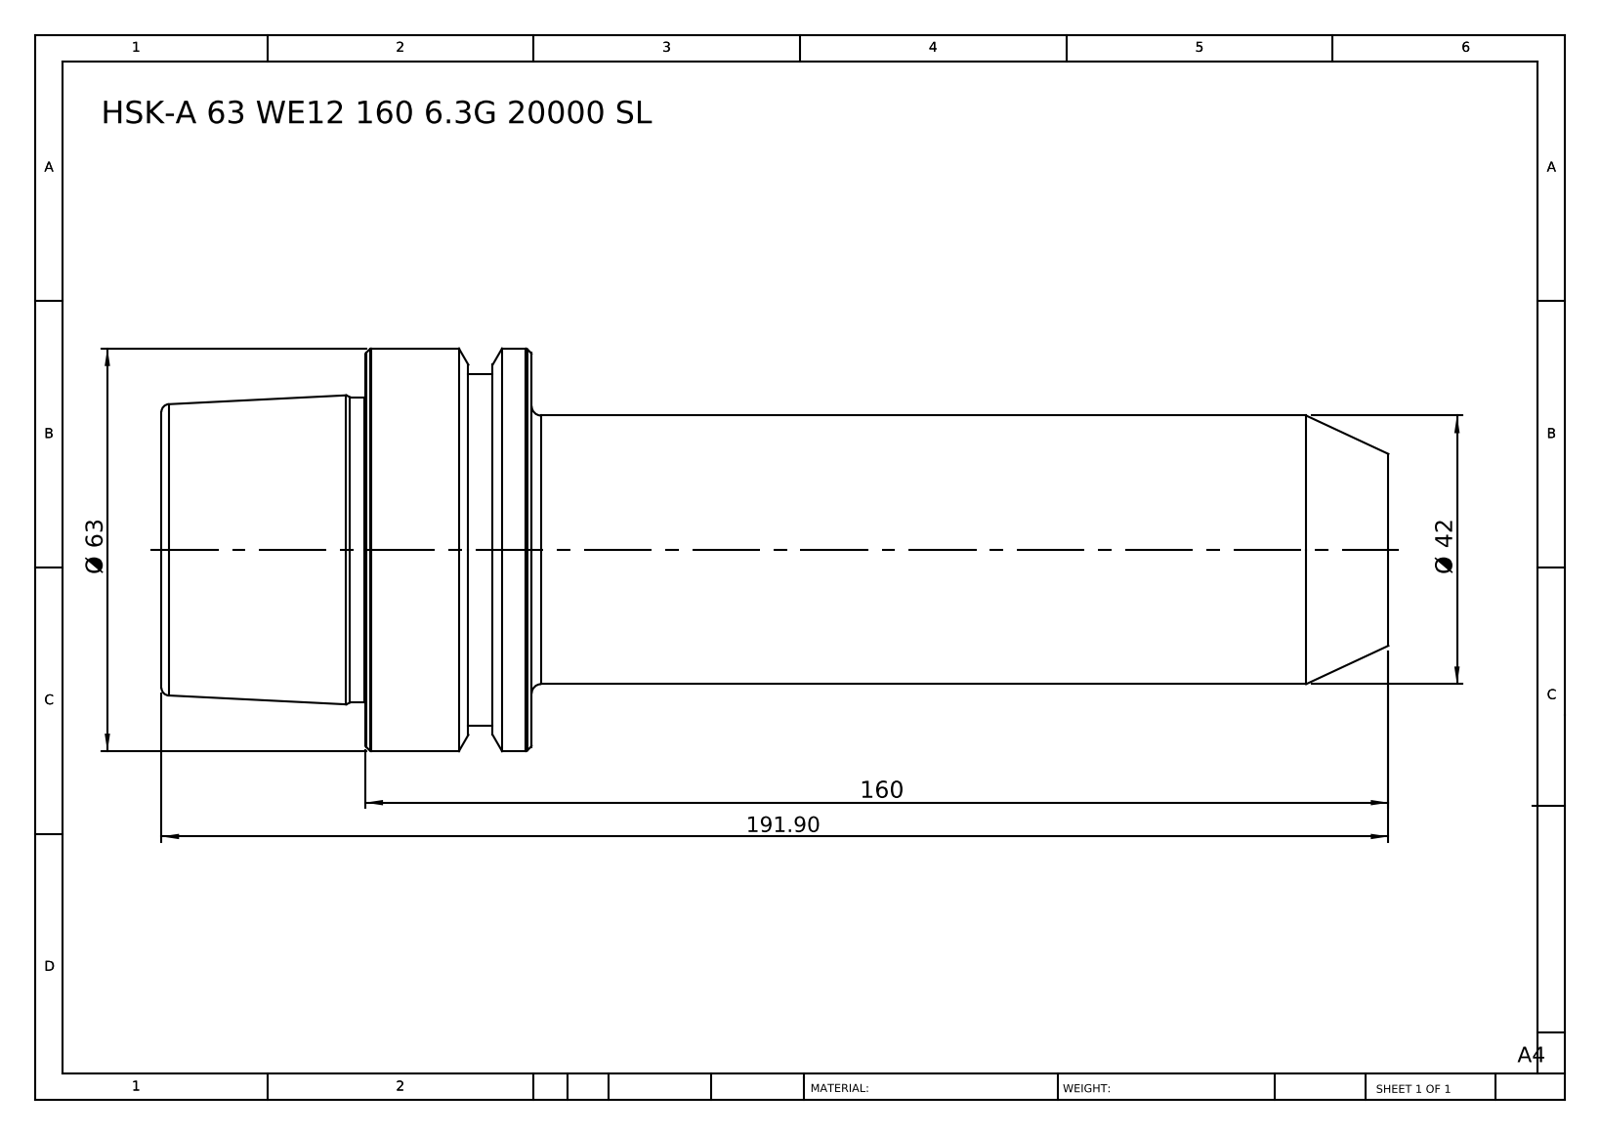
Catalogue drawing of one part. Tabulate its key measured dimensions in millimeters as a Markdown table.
| quantity | value |
| --- | --- |
| part name | HSK-A 63 WE12 160 6.3G 20000 SL |
| STEP written by | SolidWorks 2014 (CONFIG_CONTROL_DESIGN) |
| units | millimeters |
| bodies | 1 solid, 46 faces (6 planar, 10 cylindrical, 30 other) |
| overall size | 191.9 × 63 × 63 |
| volume | 313 677 mm³ |
| surface area | 33 473 mm² |
| round bosses / shafts (diameter × count) | 63 × 1, 55 × 1, 47.78 × 1, 42 × 1 |
| main face-to-face distances | 57.9, 26, 31.9, 134, 160, 191.9, 140.1, 6.1, 19.9, 51.8 |
